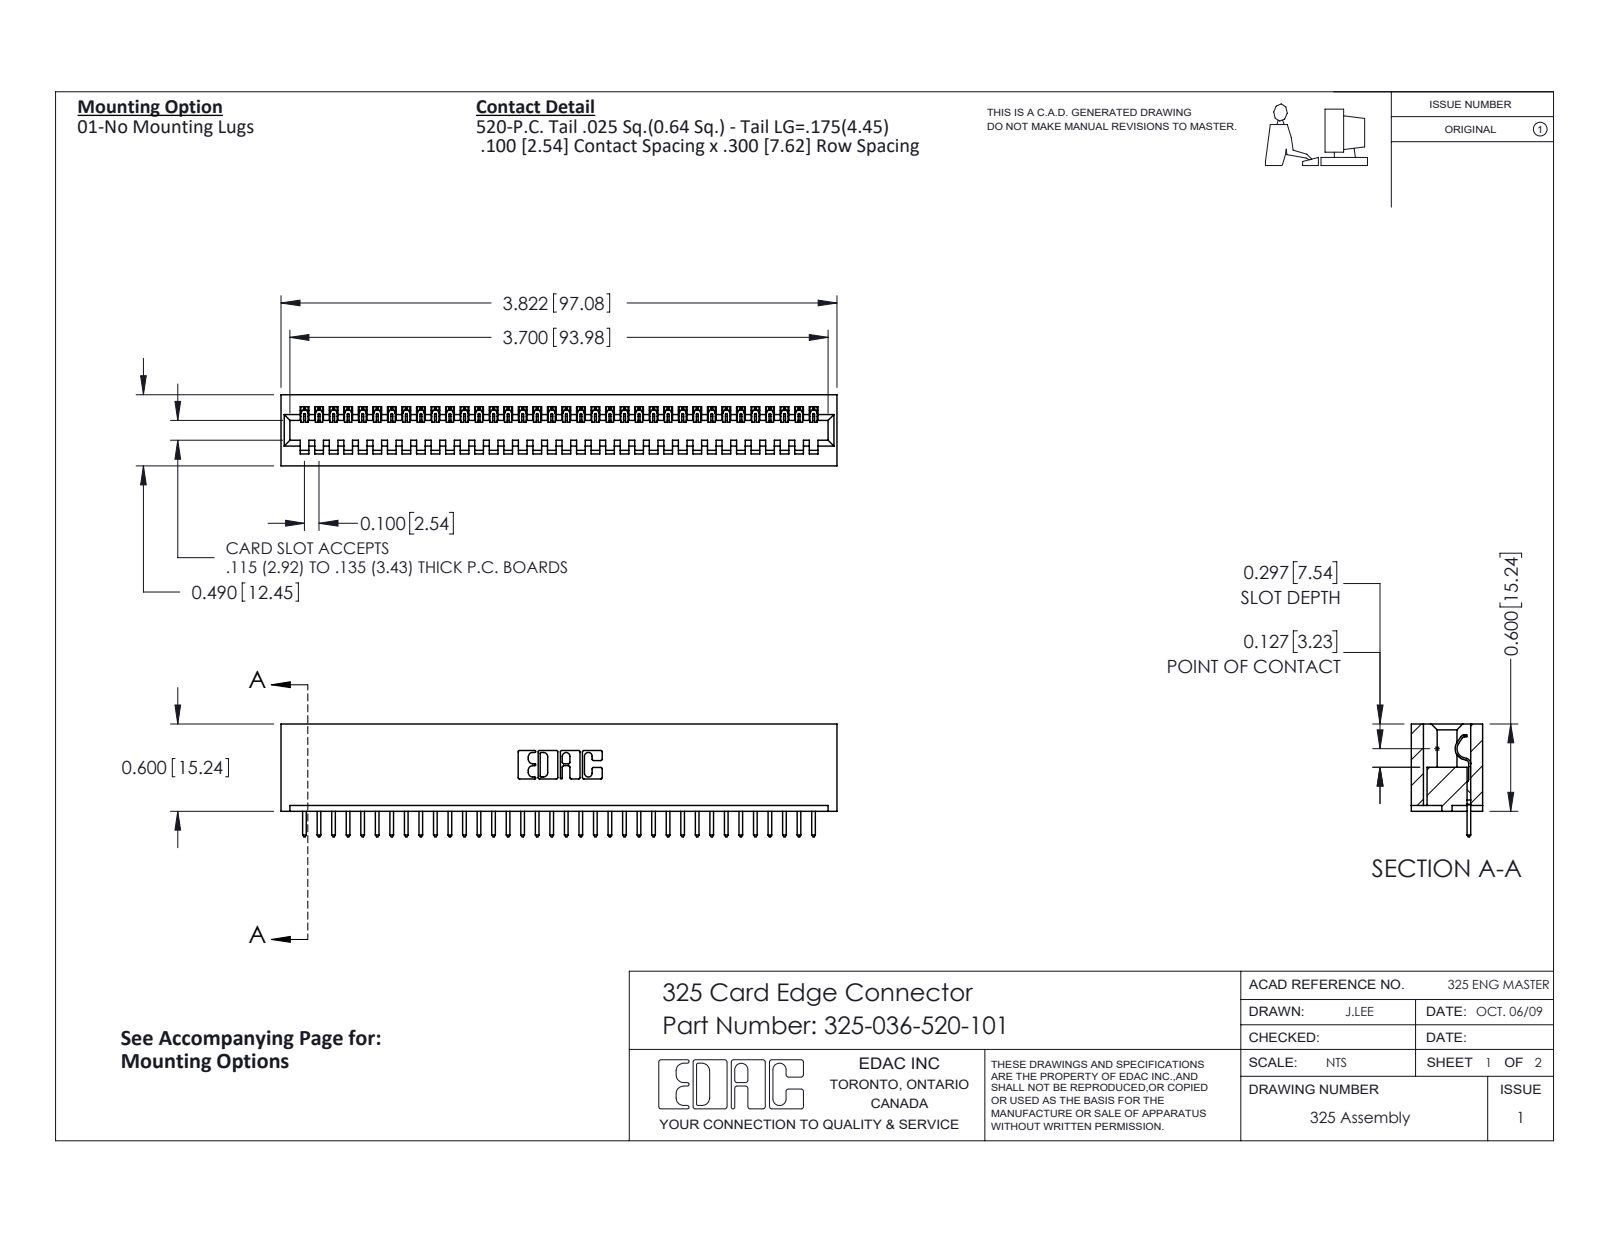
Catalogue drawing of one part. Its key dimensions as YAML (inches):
part_name: "325-036-520-101; 325 Part_Lugless; 325-292-001_325-293-120"
step_written_by: "SolidWorks 2016 (CONFIG_CONTROL_DESIGN)"
units: inches
bodies: {solids: 37, faces: 2194, planar: 1578, cylindrical: 616, other: 0}
overall_size: [3.822, 0.775, 0.49]
volume: 0.778
surface_area: 21.62
partial_cylinders:
  - {radius: 0.006, count: 72}
  - {radius: 0.01, count: 72}
  - {radius: 0.01, count: 22}
  - {radius: 0.007, count: 6}
  - {radius: 0.031, count: 6}
  - {radius: 0.026, count: 3}
  - {radius: 0.014, count: 1}
  - {radius: 0.022, count: 1}
face_to_face_distances: [0.083, 0.407, 0.49, 0.3, 0.107, 0.383, 0.025, 0.325, 0.56, 0.263]
